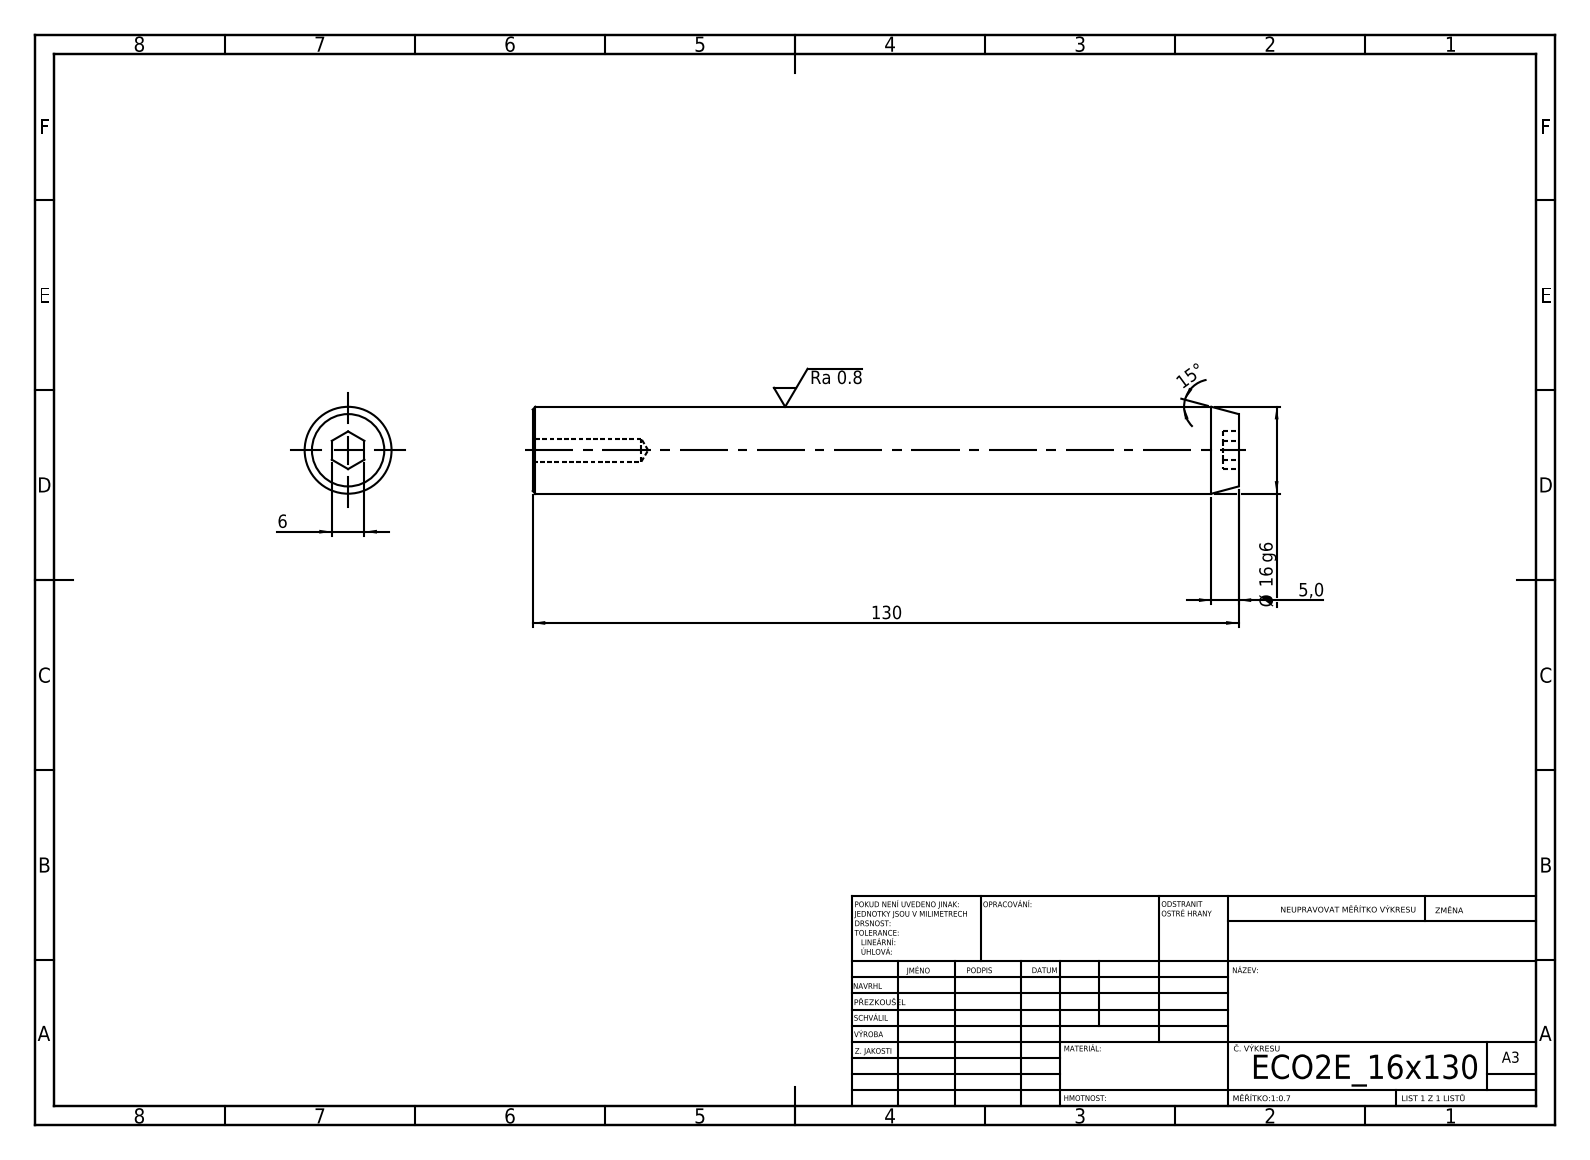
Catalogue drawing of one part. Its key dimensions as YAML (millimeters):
step_written_by: "SolidWorks 2019 (CONFIG_CONTROL_DESIGN)"
units: millimeters
bodies: {solids: 1, faces: 19, planar: 9, cylindrical: 4, other: 6}
overall_size: [130, 16, 16]
volume: 25603
surface_area: 7171
round_holes:
  - {diameter: 4.2, count: 1}
round_bosses_or_shafts:
  - {diameter: 16, count: 1}
face_to_face_distances: [130, 2.8, 127.2, 6]
